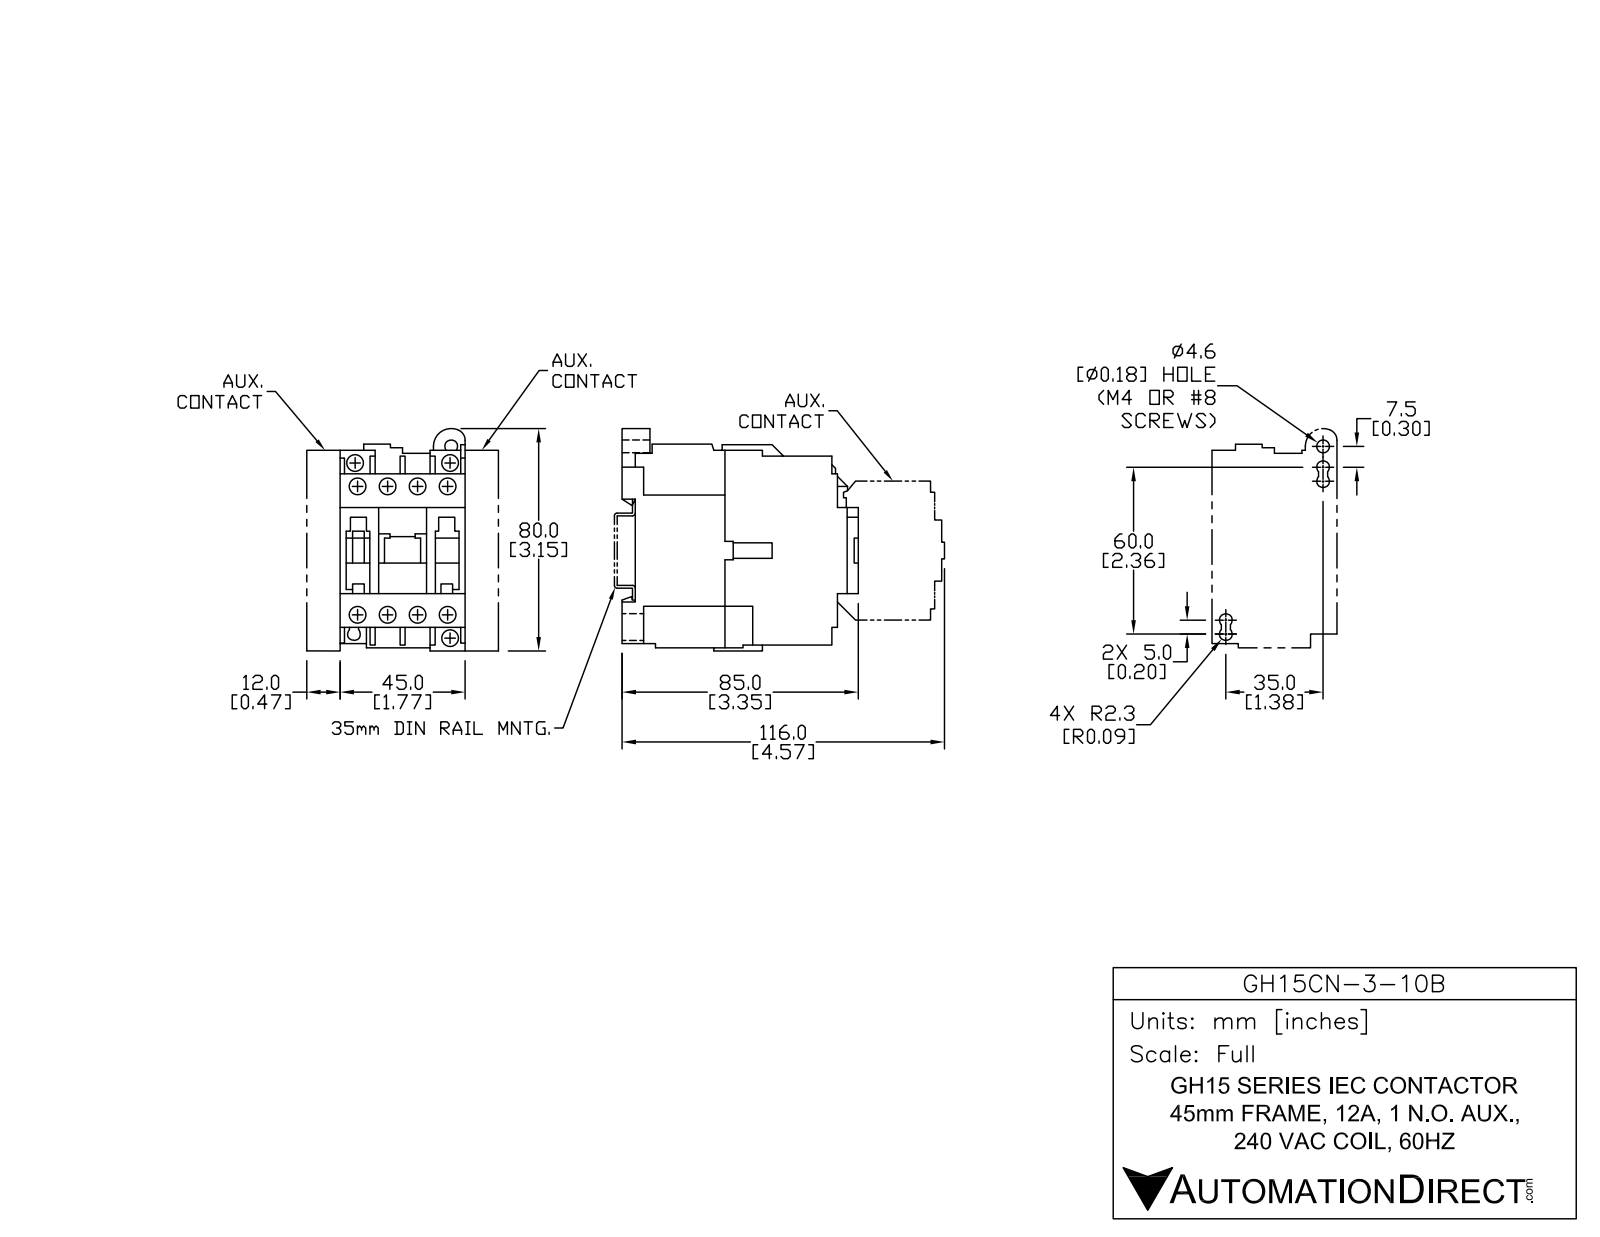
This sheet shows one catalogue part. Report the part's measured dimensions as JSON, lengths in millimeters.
{"part_name": "GH15CN-3-10B", "step_written_by": "SolidWorks 2009 (AUTOMOTIVE_DESIGN)", "units": "millimeters", "bodies": {"solids": 1, "faces": 661, "planar": 442, "cylindrical": 65, "other": 154}, "overall_size": [85.5, 80, 45], "volume_mm3": 196351, "surface_area_mm2": 35792, "round_holes": [[6.25, 9], [6.5, 2], [4.6, 1]], "partial_cylinders_radius": [[1, 10], [2.3, 8], [4.75, 8], [3, 2], [4.99, 1], [5, 1]], "face_to_face_distances": [45, 9.5, 35.5, 12.12, 23.38, 8, 7, 33.75, 10.38, 32.87], "hole_center_spacings": [11.25, 47.12, 22.5, 45.76, 50.99, 7.62, 33.75, 53.38]}
